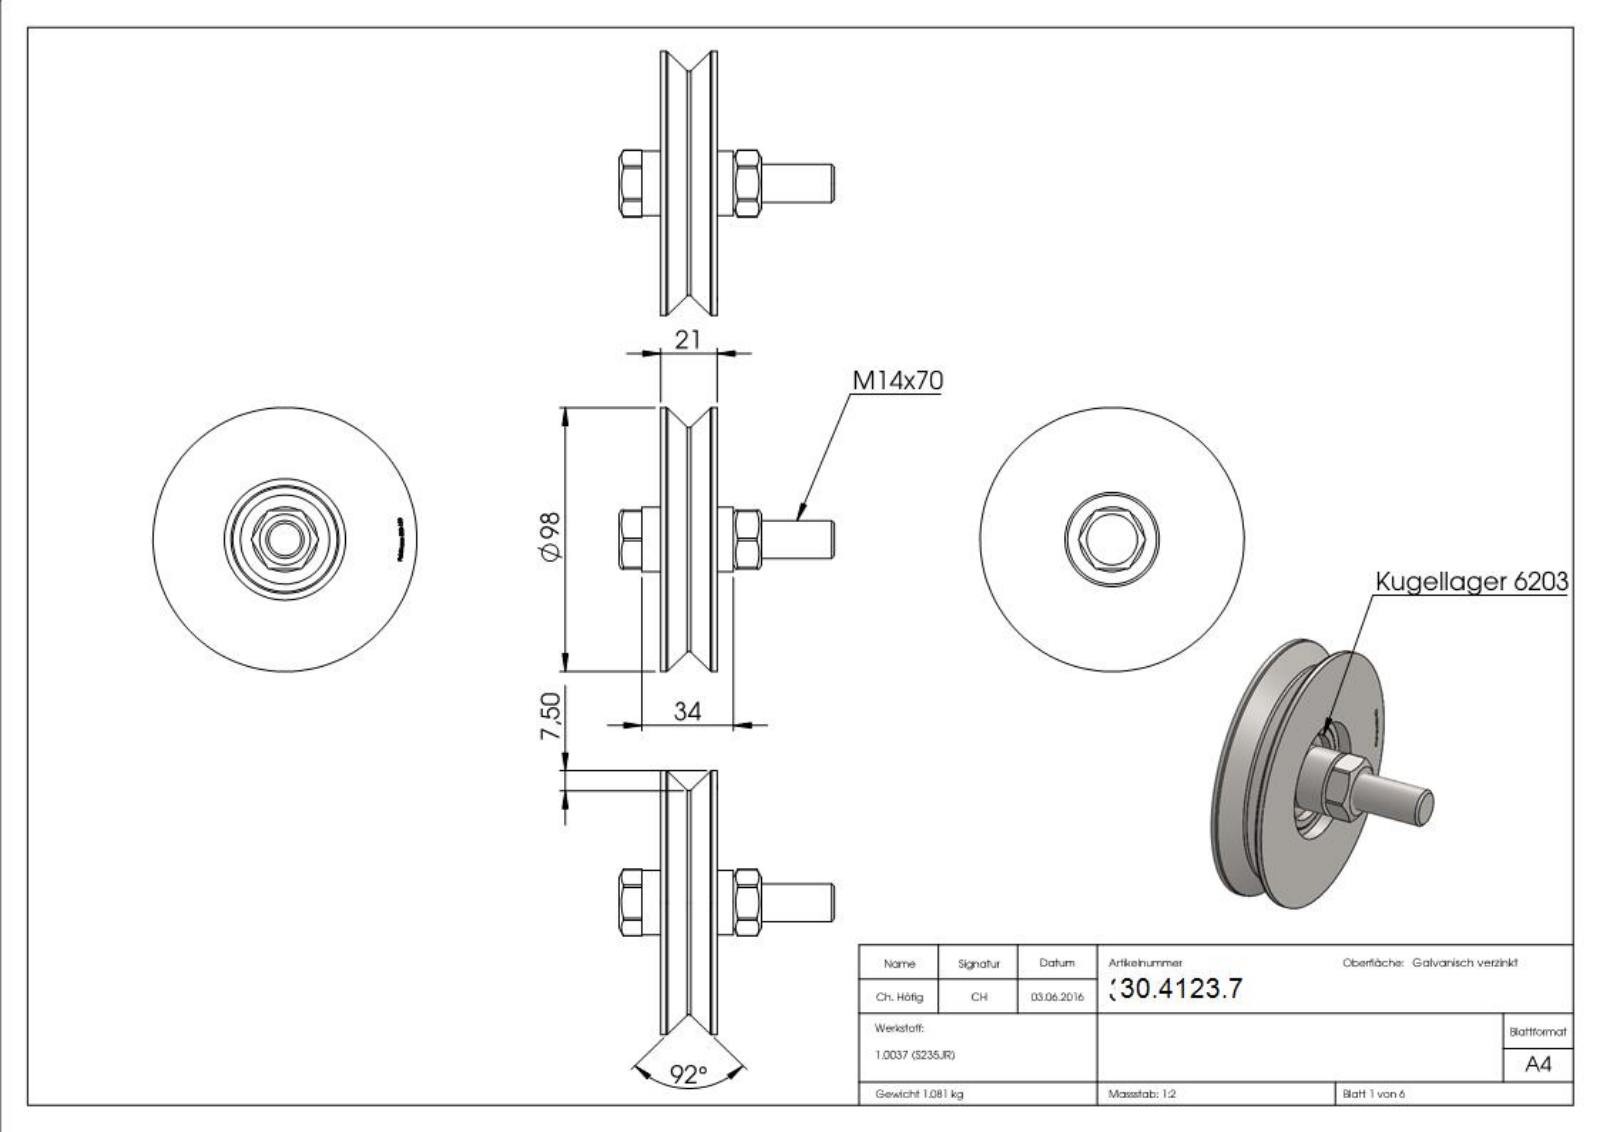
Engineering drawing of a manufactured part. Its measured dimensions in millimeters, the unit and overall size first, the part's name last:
Units: millimetres
Overall size (bounding box): 98 × 98 × 80
Round holes (diameter × count): ⌀12 ×1, ⌀14 ×1, ⌀17 ×1, ⌀33.1 ×1, ⌀35 ×1, ⌀40 ×1, ⌀45 ×1
Round bosses / shafts (diameter × count): ⌀98 ×1, ⌀24 ×1, ⌀23.9 ×1, ⌀16.85 ×1
Partial cylindrical surfaces — rounded edges, fillets, slot ends (radius × count): R1 ×6
Main face-to-face distances: 21, 16, 5, 12, 11, 4, 17, 23, 7, 28
Volume: 147 333 mm³ · Surface area: 39 907 mm²
Bodies: 6 solids, 264 faces (120 planar, 31 cylindrical, 113 other)
Part name (STEP PRODUCT): radial ball bearing_68_din_DIN 625 - 6203 - 10,SI,NC,10_68; 300-100 Teil5_300-120-U Teil5; radial ball bearing_68_din; 300-100 Teil5 (+7 more)
STEP written by: SolidWorks 2018 (CONFIG_CONTROL_DESIGN)
